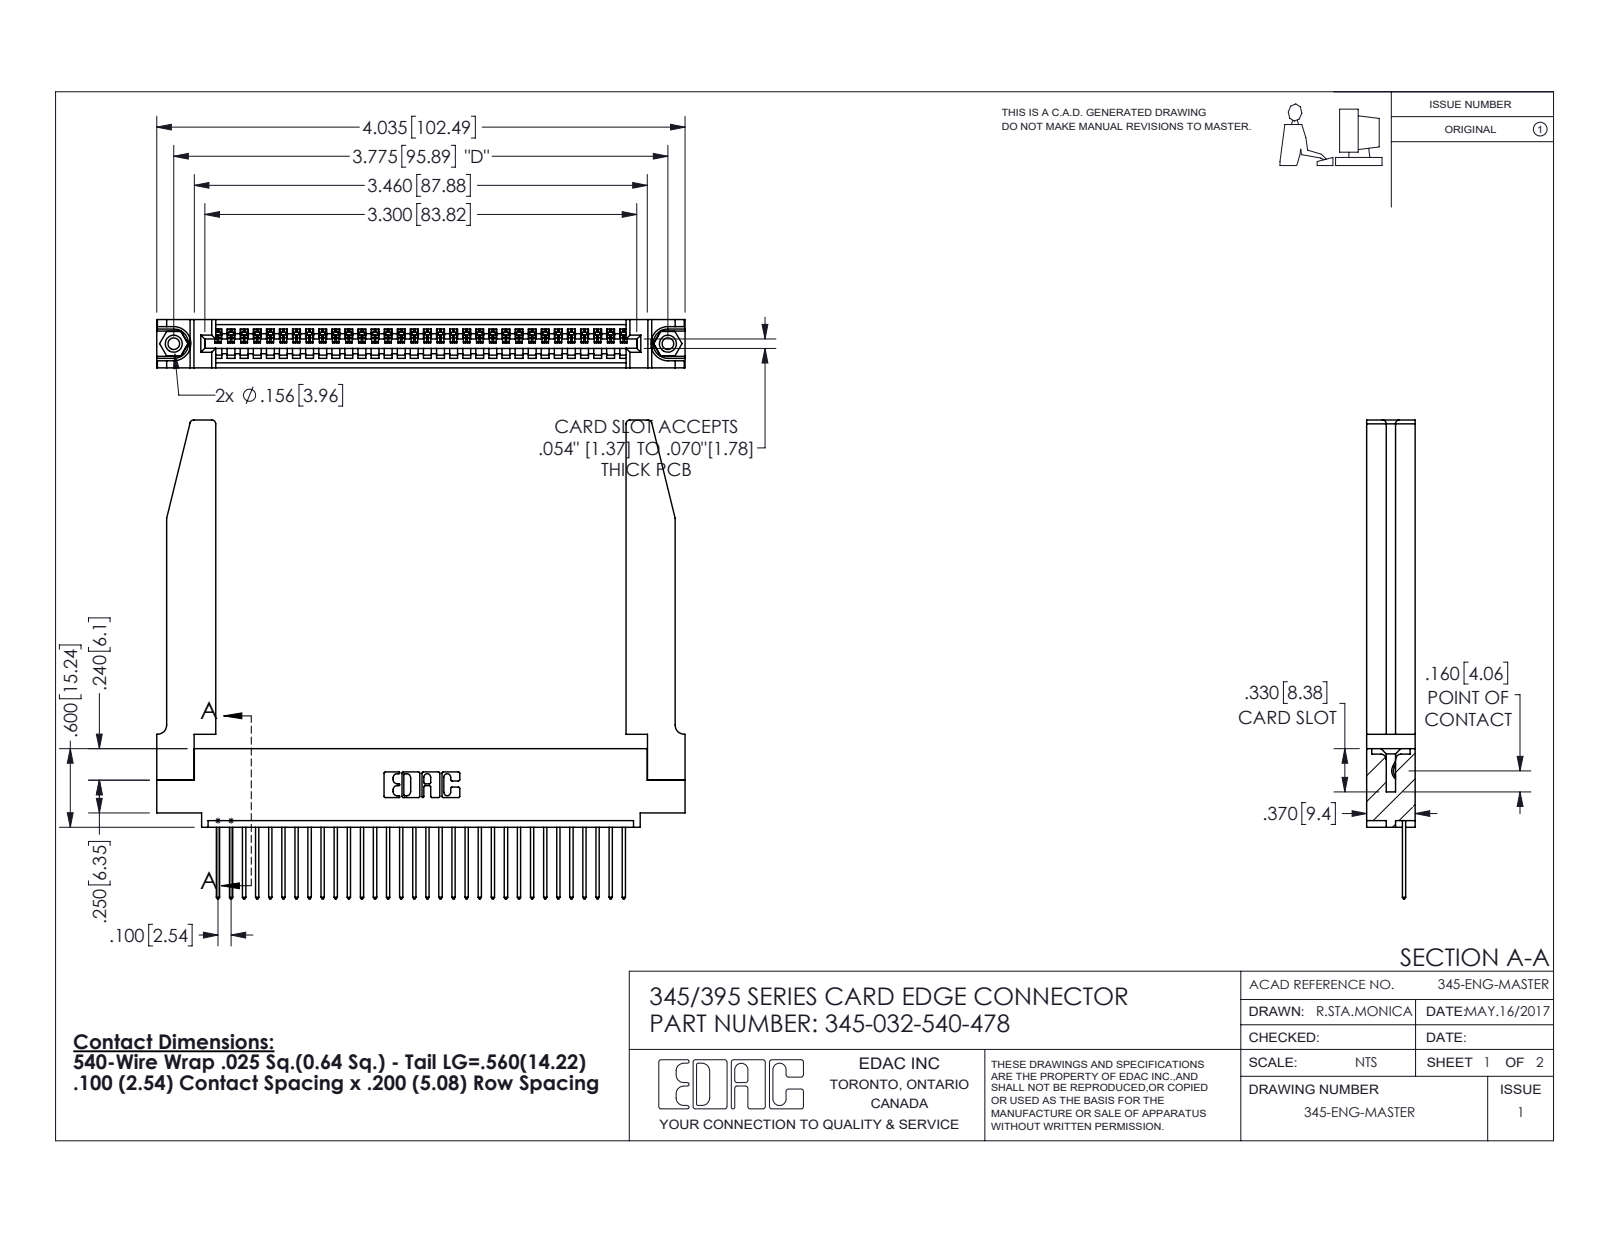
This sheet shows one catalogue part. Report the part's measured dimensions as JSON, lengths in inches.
{"part_name": "345-032-540-478; 345-220-078_345-220-078; 345-250-001_345-250-001-102; 345-292-001_345-293-140 (+1 more)", "step_written_by": "SolidWorks 2016 (CONFIG_CONTROL_DESIGN)", "units": "inches", "bodies": {"solids": 37, "faces": 2220, "planar": 1506, "cylindrical": 662, "other": 52}, "overall_size": [4.036, 3.657, 0.37], "volume_in3": 1.062, "surface_area_in2": 30.84, "round_holes": [[0.089, 2], [0.125, 2], [0.156, 2], [0.064, 1]], "round_bosses_or_shafts": [[0.155, 2]], "partial_cylinders_radius": [[0.006, 64], [0.01, 64], [0.01, 22], [0.03, 8], [0.007, 6], [0.031, 6], [0.026, 3], [0.031, 2]], "face_to_face_distances": [0.37, 0.072, 0.298, 0.098, 0.272, 0.025, 0.2, 0.148, 0.15, 0.225], "hole_center_spacings": [0.27, 3.54, 3.775]}
